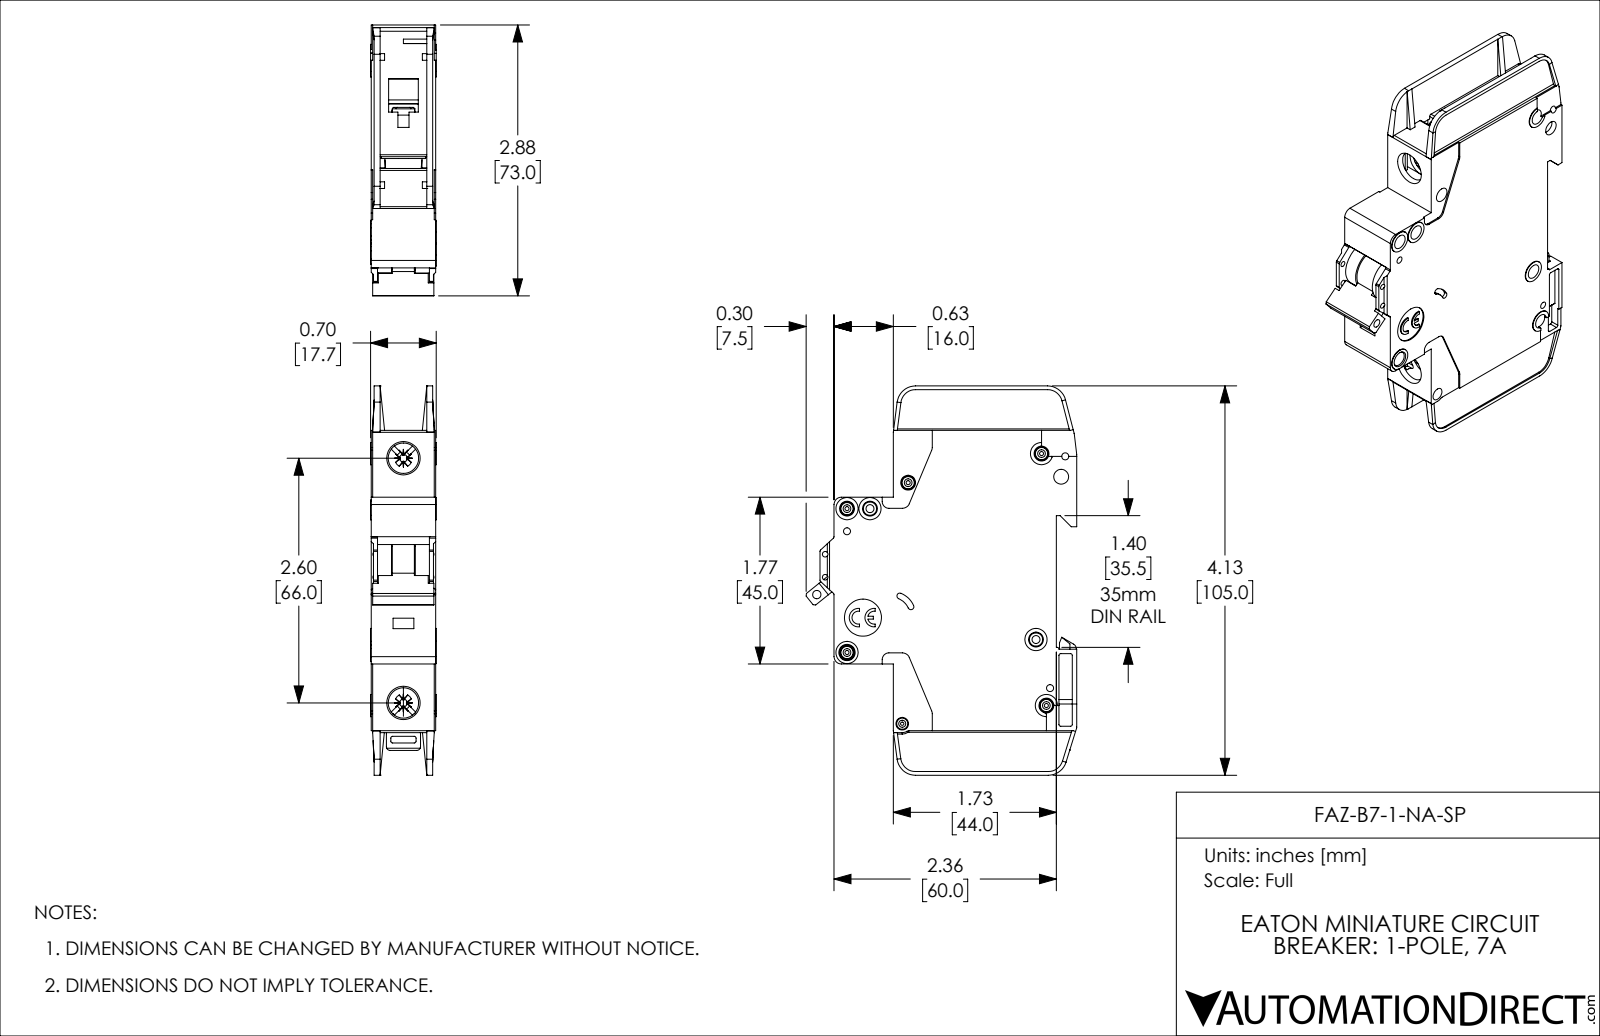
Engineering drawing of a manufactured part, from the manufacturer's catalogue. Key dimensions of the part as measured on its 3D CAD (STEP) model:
Part name (STEP PRODUCT): FAZ-B7-1-NA-SP
STEP written by: SolidWorks 2019 (AUTOMOTIVE_DESIGN)
Units: inches
Bodies: 1 solid, 1127 faces (671 planar, 357 cylindrical, 99 other)
Overall size (bounding box): 4.134 × 2.876 × 0.697
Volume: 4.682 in³ · Surface area: 41.01 in²
Round holes (diameter × count): ⌀0.157 ×8, ⌀0.043 ×5, ⌀0.075 ×4, ⌀0.059 ×2, ⌀0.085 ×2, ⌀0.323 ×2, ⌀0.035 ×1, ⌀0.089 ×1, ⌀0.098 ×1, ⌀0.134 ×1, ⌀0.394 ×1
Round bosses / shafts (diameter × count): ⌀0.13 ×5, ⌀0.236 ×4, ⌀0.118 ×2, ⌀0.098 ×1
Partial cylindrical surfaces — rounded edges, fillets, slot ends (radius × count): R0.02 ×42, R0.016 ×10, R0.039 ×10, R0.079 ×8, R0.197 ×5, R0.008 ×4, R0.026 ×4, R0.043 ×4
Main face-to-face distances: 0.047, 0.685, 0.591, 0.638, 0.094, 0.543, 0.016, 0.031, 0.496, 0.575
Hole centre spacings: 0.244, 0.537, 0.87, 0.189, 0.199, 0.204, 0.221, 0.24
